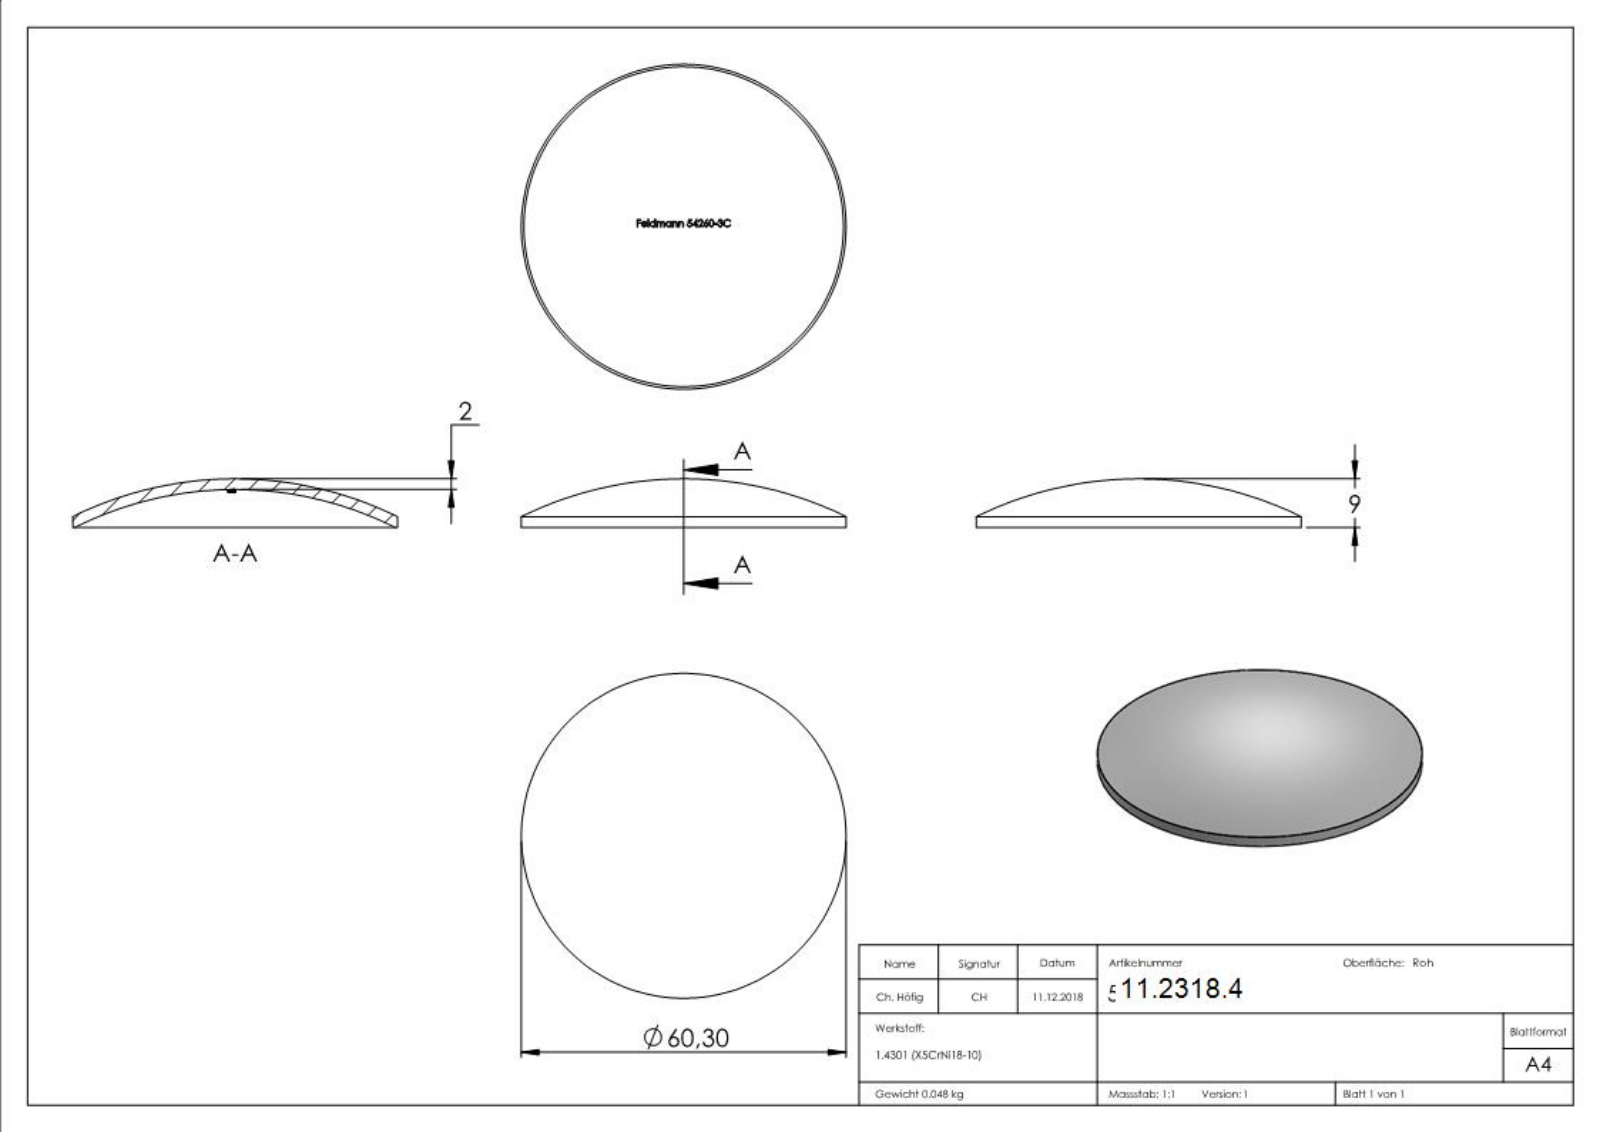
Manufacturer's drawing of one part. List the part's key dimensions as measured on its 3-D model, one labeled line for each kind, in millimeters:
Part name (STEP PRODUCT): 54260-3C
STEP written by: SolidWorks 2015 (CONFIG_CONTROL_DESIGN)
Units: millimetres
Bodies: 1 solid, 237 faces (92 planar, 2 cylindrical, 143 other)
Overall size (bounding box): 60.3 × 60.3 × 9
Volume: 6 019 mm³ · Surface area: 6 408 mm²
Round bosses / shafts (diameter × count): ⌀60.3 ×1
Main face-to-face distances: 0.39, 2.97, 1.12, 2.02, 1.25, 8.92, 1.64, 0.44, 4.09, 7.67
